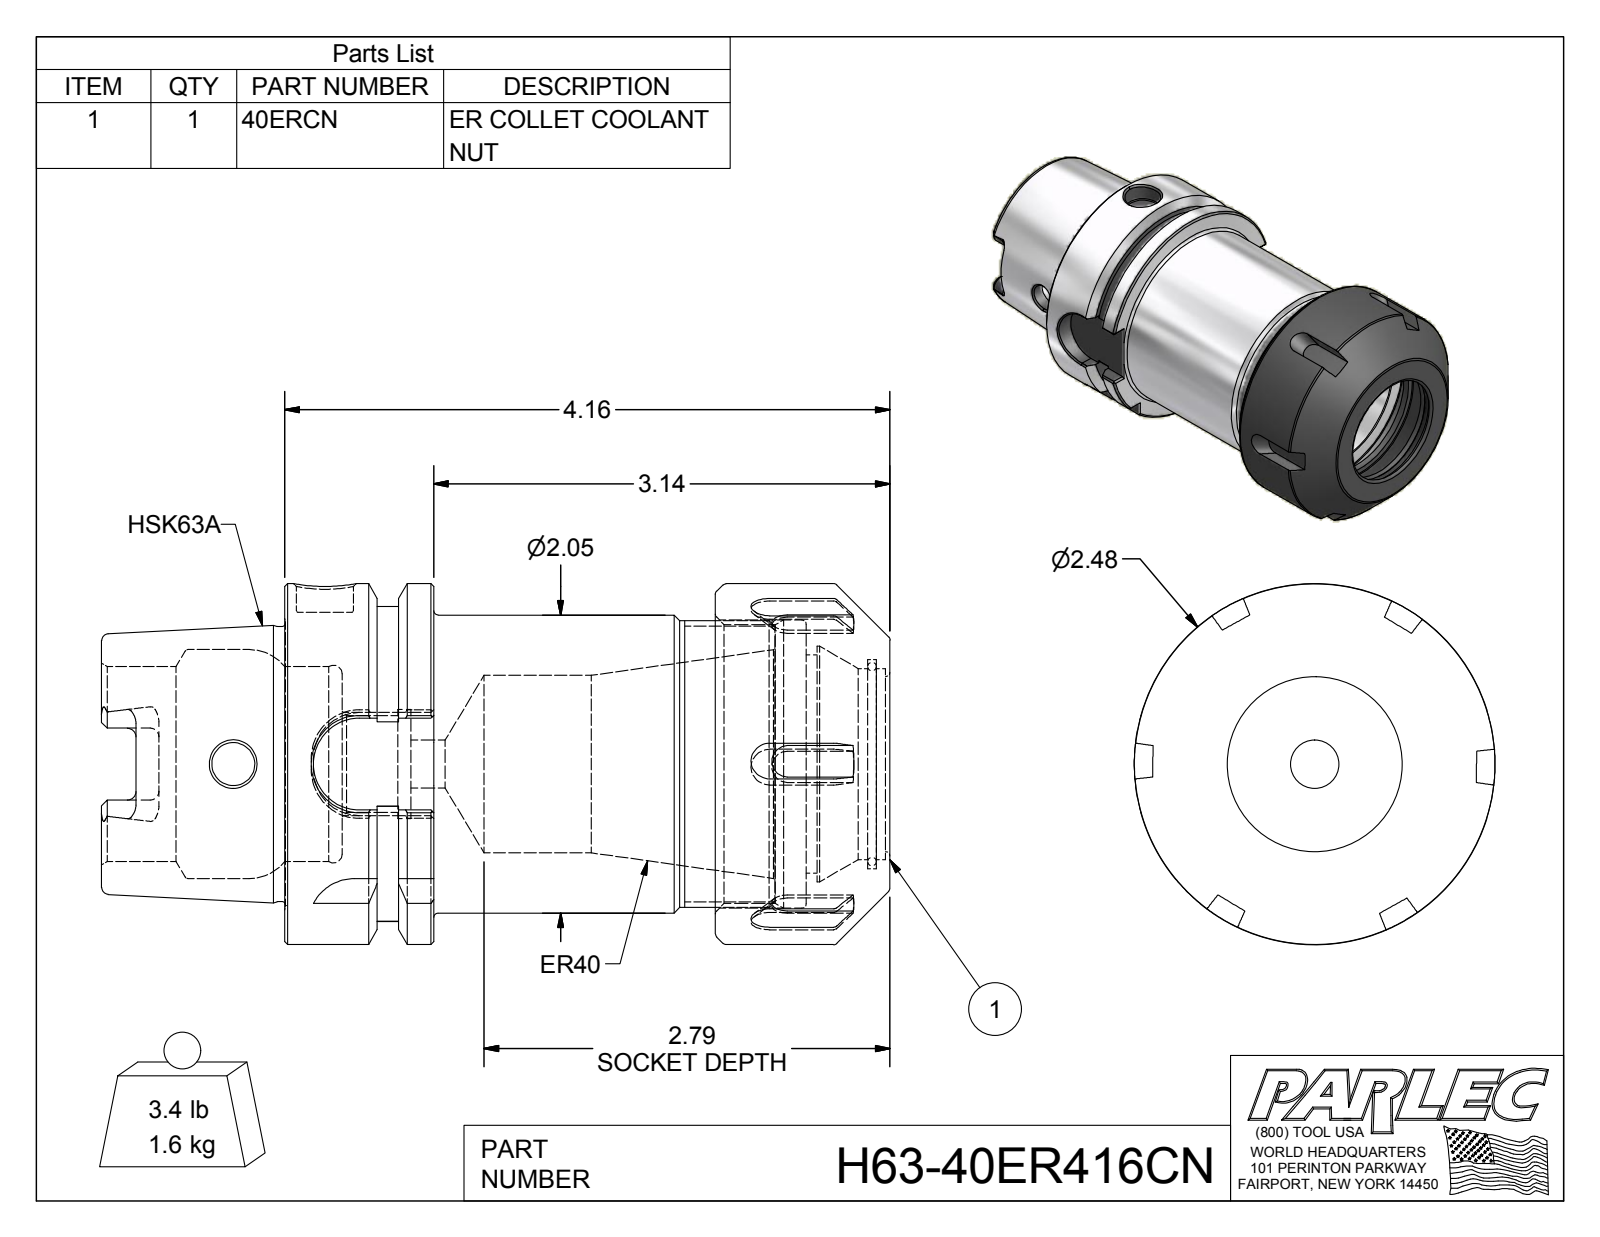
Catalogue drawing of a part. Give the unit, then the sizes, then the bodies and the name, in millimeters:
Units: millimetres
Overall size (bounding box): 137.7 × 63 × 63
Round holes (diameter × count): ⌀7.5 ×1, ⌀8.4 ×1, ⌀10 ×1, ⌀16.9 ×1, ⌀19 ×1, ⌀31 ×1, ⌀33.4 ×1, ⌀34 ×1, ⌀36.5 ×1, ⌀38.1 ×1, ⌀40 ×1, ⌀41.1 ×1
Round bosses / shafts (diameter × count): ⌀63 ×1, ⌀63 ×1, ⌀52 ×1, ⌀50 ×1, ⌀48 ×1
Partial cylindrical surfaces — rounded edges, fillets, slot ends (radius × count): R1.5 ×6, R2.9 ×4, R8 ×4, R27.5 ×1
Main face-to-face distances: 91.1, 26, 105.7, 14.6, 6.1, 9.9, 65, 79.7, 75.2, 49.2
Volume: 196 300 mm³ · Surface area: 51 660 mm²
Bodies: 2 solids, 200 faces (82 planar, 44 cylindrical, 74 other)
Part name (STEP PRODUCT): H63-40ER416CN; H63-40ER4-1; 40ERCN
STEP written by: Autodesk Inventor 2012 (AUTOMOTIVE_DESIGN)
